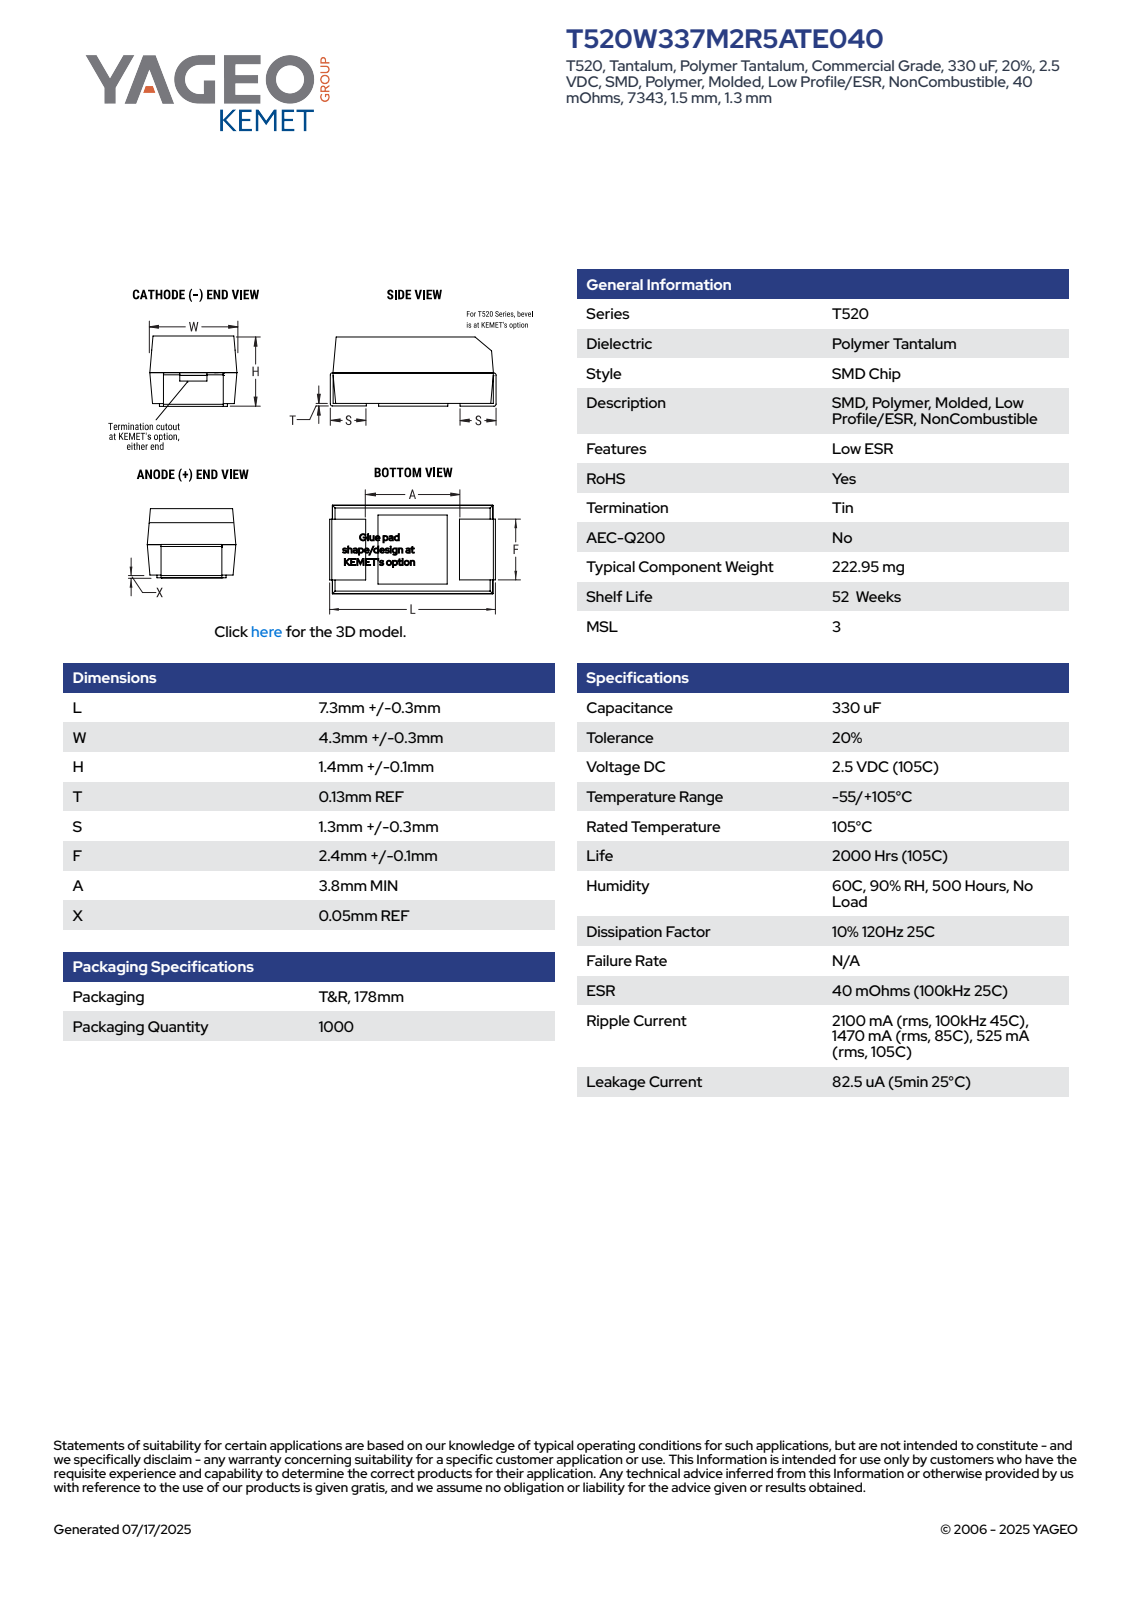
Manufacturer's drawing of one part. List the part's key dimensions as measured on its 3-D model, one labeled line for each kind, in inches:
Part name (STEP PRODUCT): CTS_TCM2NOBNOKBOPT_7343_L7.6W4.6H1.5T0.13S1.3F2.5A3.6X0.05
STEP written by: SolidWorks 2014 (AUTOMOTIVE_DESIGN)
Units: inches
Bodies: 4 solids, 90 faces (86 planar, 4 cylindrical, 0 other)
Overall size (bounding box): 0.299 × 0.181 × 0.059
Volume: 0.003 in³ · Surface area: 0.166 in²
Partial cylindrical surfaces — rounded edges, fillets, slot ends (radius × count): R0.005 ×4
Main face-to-face distances: 0.056, 0.054, 0.177, 0.059, 0.277, 0.277, 0.294, 0.289, 0.299, 0.046
